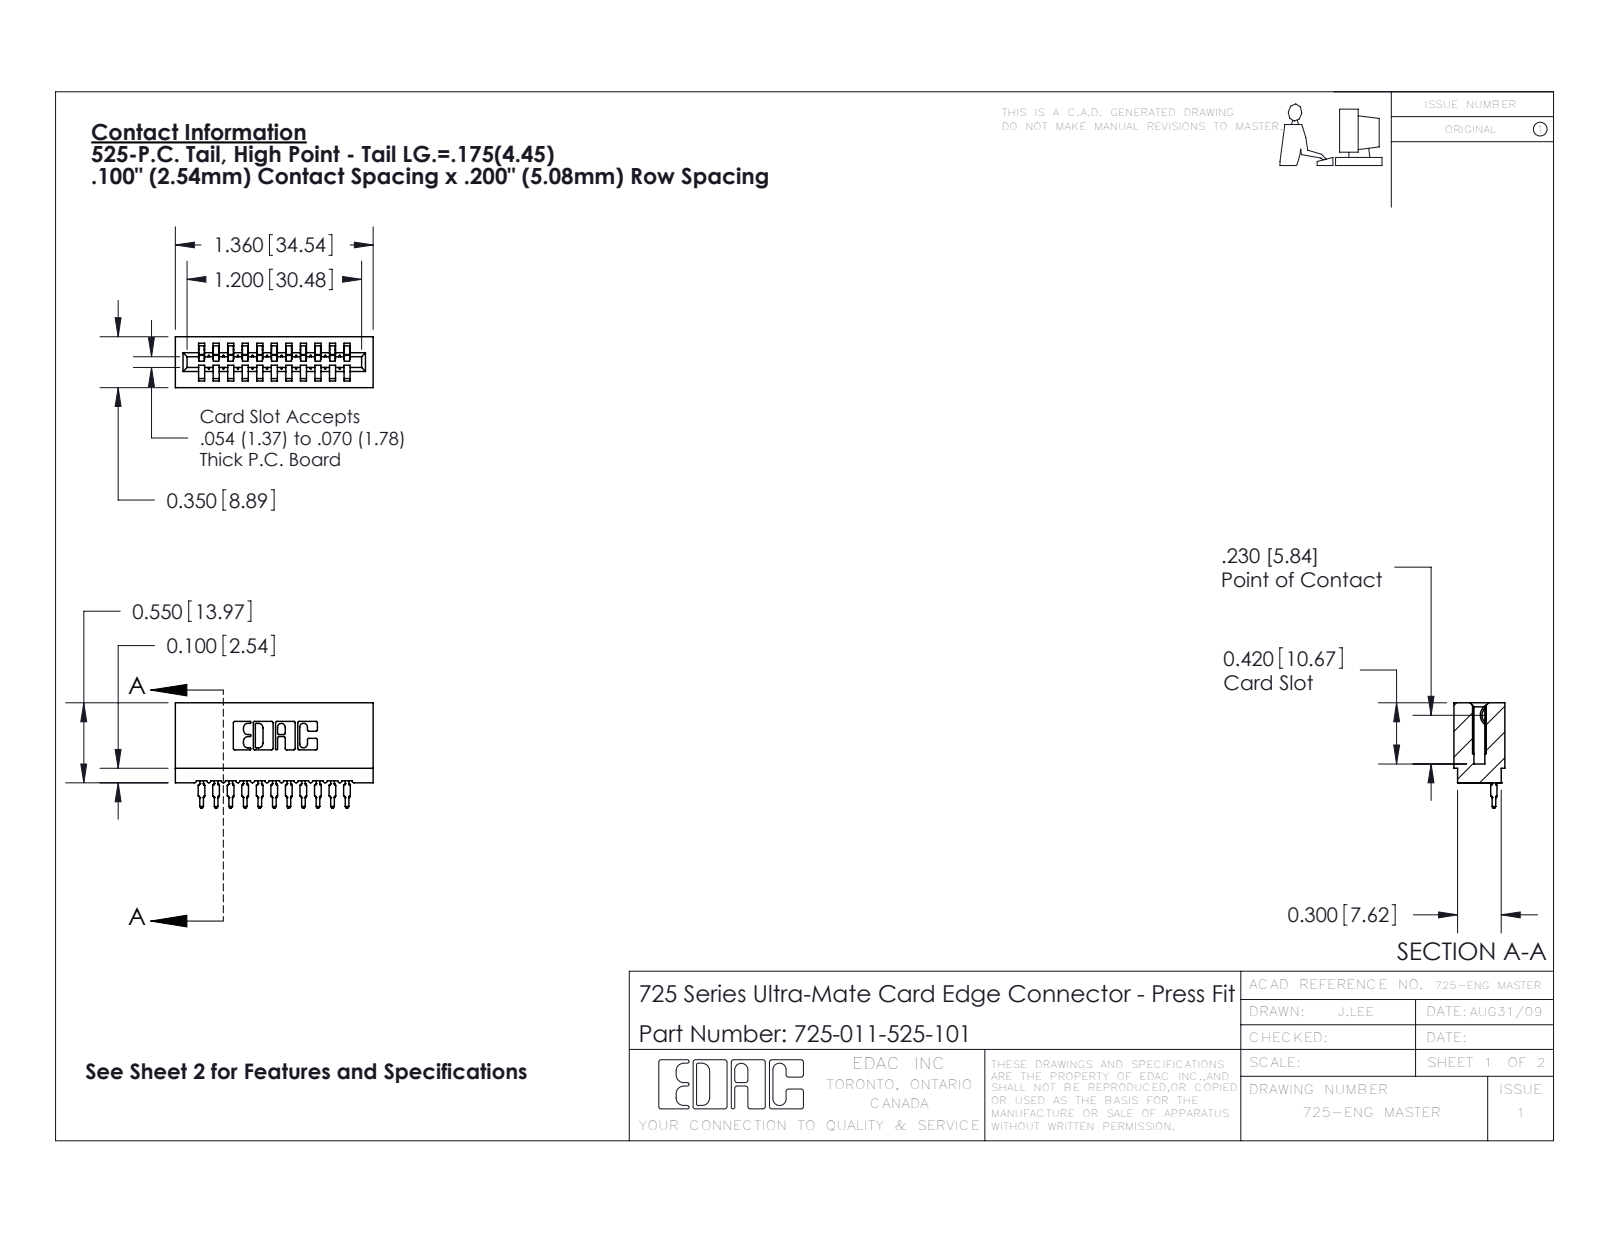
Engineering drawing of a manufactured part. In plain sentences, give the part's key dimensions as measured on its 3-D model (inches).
The part is named "725-011-525-101; 725 Part_Insulator Option - 01; 745-292-001_525". Its 3-D file was written by "SolidWorks 2016 (CONFIG_CONTROL_DESIGN)". It is 12 solids with 1327 faces: 792 planar, 249 cylindrical and 286 other. Overall it measures 1.36 by 0.725 by 0.35 inches. Its volume is 0.17 cubic inches and its surface area 7.388 square inches. Partial cylindrical surfaces (rounded edges, fillets, slot ends): 22 of radius 0.01, 22 of radius 0.015, 22 of radius 0.021, 6 of radius 0.007, 6 of radius 0.031, 4 of radius 0.005, 4 of radius 0.011, 3 of radius 0.026. The main face-to-face distances are 0.1, 0.2, 0.3, 0.4, 0.5, 0.158, 0.058, 0.042, 0.142, 0.258.
